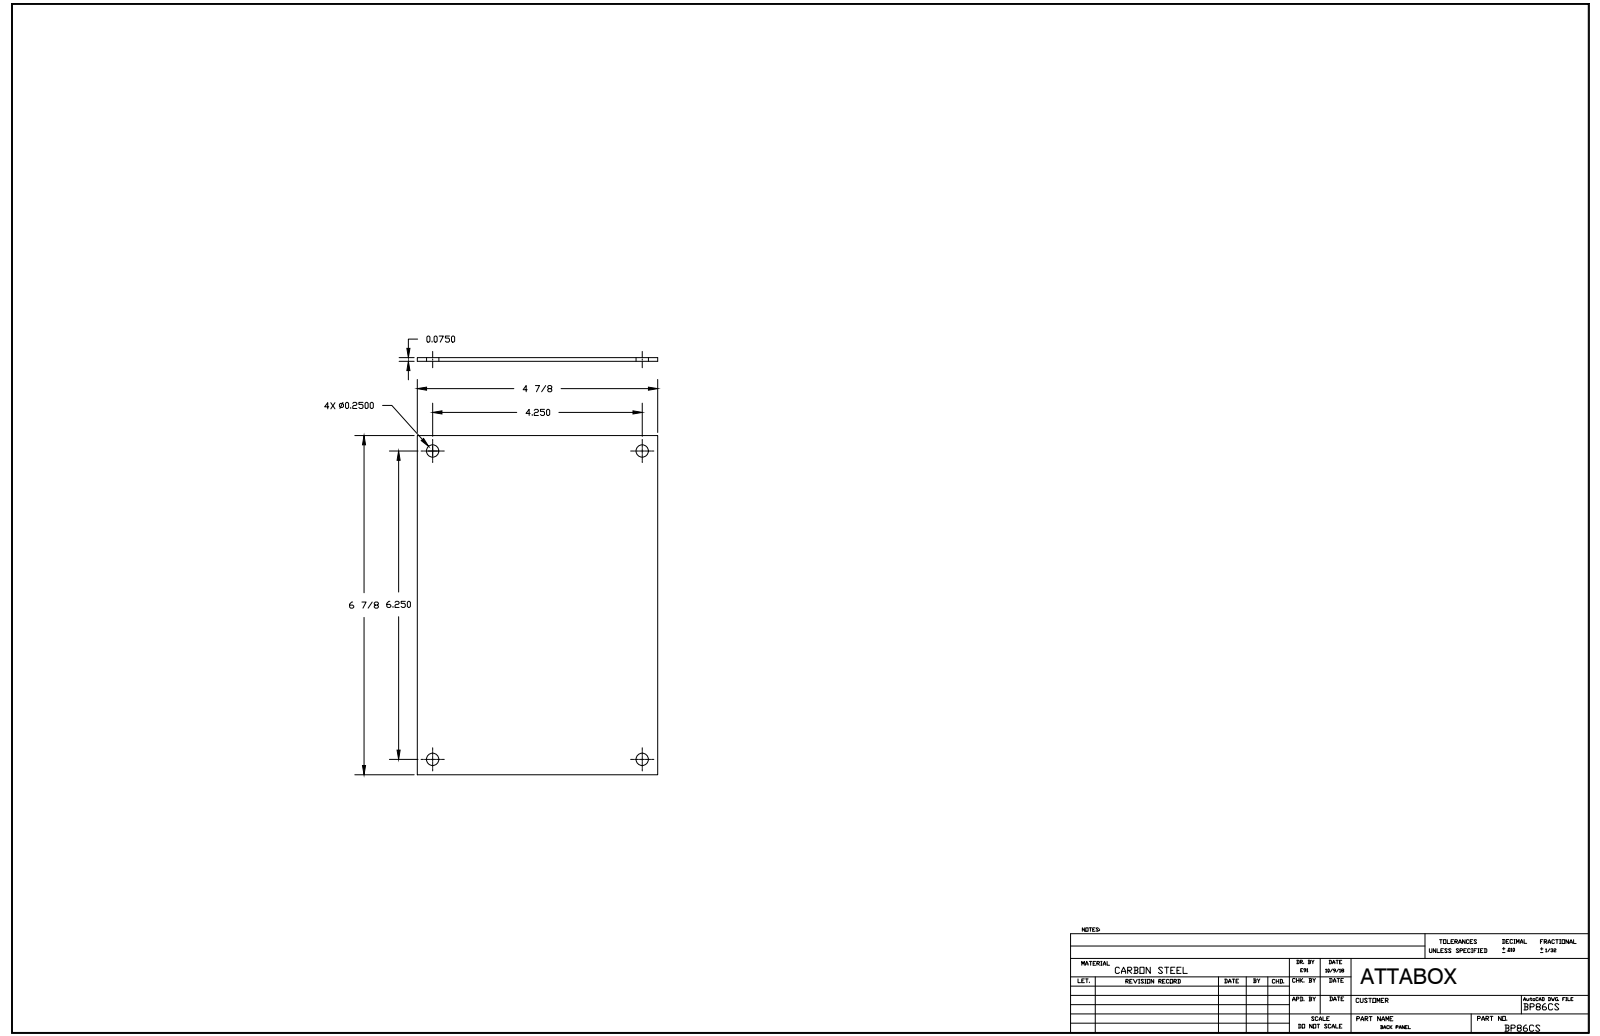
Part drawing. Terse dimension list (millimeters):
name: BP86CS_STP
written by: Autodesk Inventor 2014 (AUTOMOTIVE_DESIGN)
unit: mm
bodies: 1 solid, 10 faces (6 planar, 4 cylindrical, 0 other)
size: 174.62 × 123.83 × 1.91
volume: 40 950 mm³; area: 44 282 mm²
holes: 4× ⌀6.35
face distances: 1.9, 123.82, 174.62
hole spacings: 107.94, 158.76, 191.98
